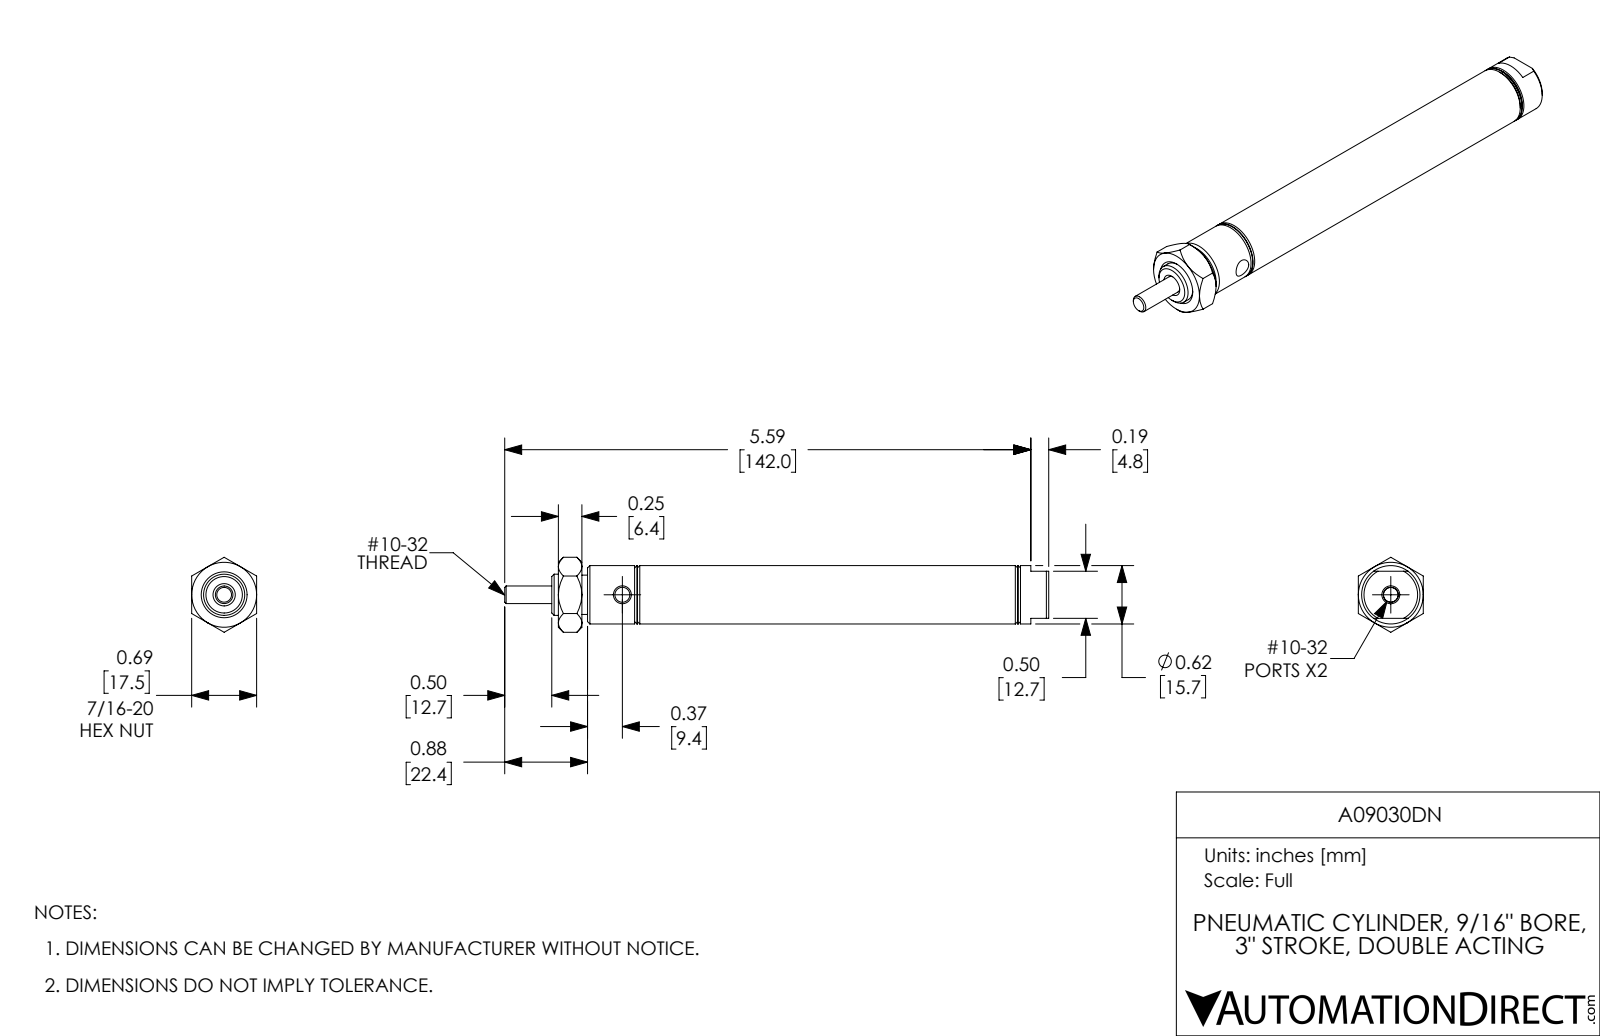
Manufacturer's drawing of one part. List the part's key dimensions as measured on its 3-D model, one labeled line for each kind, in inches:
Part name (STEP PRODUCT): A09030DN; A09030DN_Mounting Nut_D-154; A09030DN-Rod; A09030DN-MainBody
STEP written by: SolidWorks 2017 (AUTOMOTIVE_DESIGN)
Units: inches
Bodies: 3 solids, 100 faces (28 planar, 34 cylindrical, 38 other)
Overall size (bounding box): 5.78 × 0.797 × 0.69
Volume: 0.919 in³ · Surface area: 23.94 in²
Round holes (diameter × count): ⌀0.159 ×2, ⌀0.19 ×2, ⌀0.156 ×1, ⌀0.187 ×1, ⌀0.437 ×1, ⌀0.563 ×1
Round bosses / shafts (diameter × count): ⌀0.62 ×1, ⌀0.417 ×1
Main face-to-face distances: 0.7, 4.2, 0.5, 0.69, 3.5, 4.96, 4.26, 0.76, 1.2, 3
